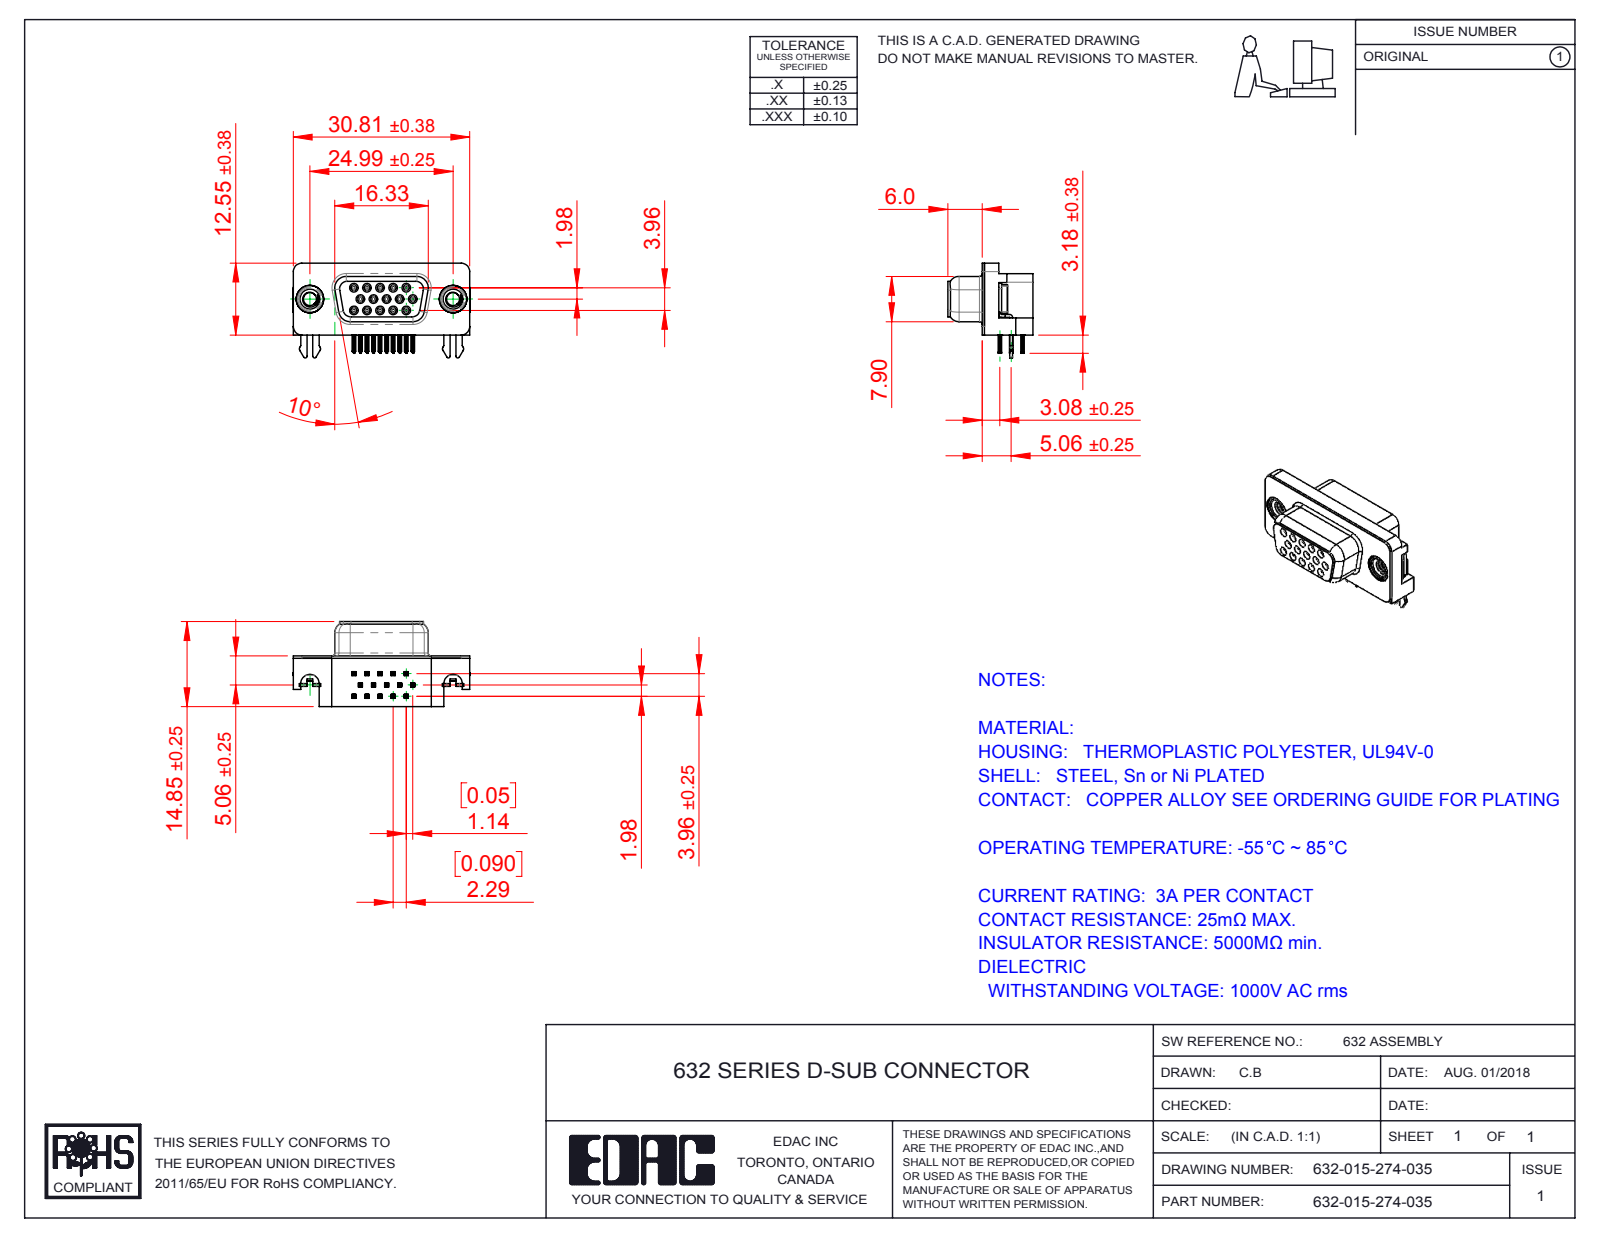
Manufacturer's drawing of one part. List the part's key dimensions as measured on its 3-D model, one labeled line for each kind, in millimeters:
Part name (STEP PRODUCT): 632 Contact Middle_Recessed; 632 Contact Bottom; 632 2 Prong Board Lock; 632 Shell_9 Socket (+6 more)
STEP written by: SolidWorks 2016 (CONFIG_CONTROL_DESIGN)
Units: millimetres
Bodies: 23 solids, 2426 faces (1006 planar, 654 cylindrical, 766 other)
Overall size (bounding box): 30.89 × 16.55 × 14.85
Volume: 2 996 mm³ · Surface area: 5 339 mm²
Round holes (diameter × count): ⌀0.8 ×15, ⌀0.9 ×15, ⌀2.26 ×2, ⌀2.5 ×2, ⌀4 ×2, ⌀4.8 ×2, ⌀5 ×2
Round bosses / shafts (diameter × count): ⌀1.2 ×15, ⌀4.9 ×2, ⌀4.75 ×2, ⌀3.9 ×2
Partial cylindrical surfaces — rounded edges, fillets, slot ends (radius × count): R0.1 ×120, R0.15 ×60, R0.35 ×30, R0.34 ×15, R1 ×11, R0.28 ×10, R0.5 ×10, R0.25 ×8
Main face-to-face distances: 0.4, 8.45, 8.85, 1.98, 2.9, 5.95, 2.5, 6.4, 6.7, 7.05
Hole centre spacings: 2.28, 2.29, 3.96, 4.57, 6.05, 3.97, 4.58, 6.86
